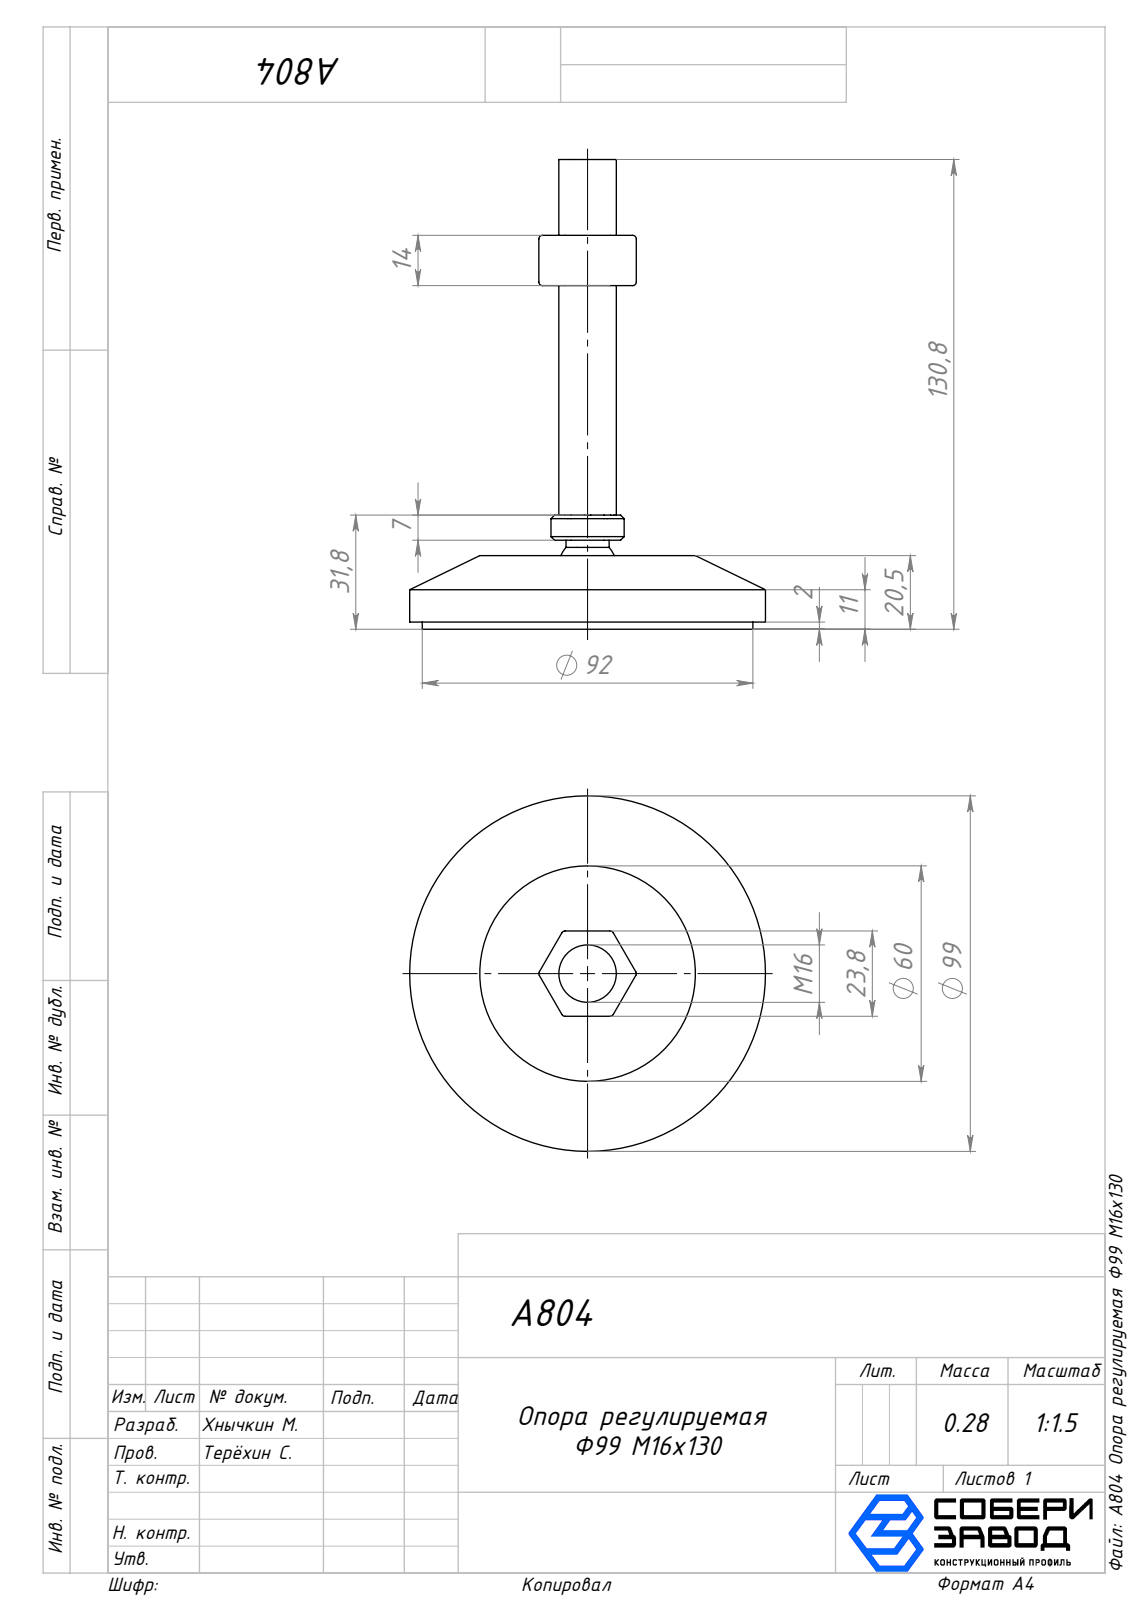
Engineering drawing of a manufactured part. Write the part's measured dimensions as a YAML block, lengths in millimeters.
part_name: "A804 Опора регулируемая Ф99 М16х130; Опора_00; Шарнирный вал M16_00; Гайка М16_00"
step_written_by: "SolidWorks 2025 (AUTOMOTIVE_DESIGN)"
units: millimeters
bodies: {solids: 3, faces: 111, planar: 37, cylindrical: 38, other: 36}
overall_size: [130.79, 99, 99]
volume: 157594
surface_area: 28495
round_holes:
  - {diameter: 14, count: 1}
  - {diameter: 16, count: 1}
round_bosses_or_shafts:
  - {diameter: 99, count: 1}
  - {diameter: 92, count: 1}
  - {diameter: 12, count: 1}
partial_cylinders:
  - {radius: 1, count: 24}
face_to_face_distances: [20.5, 2, 18.5, 23.74, 2.92, 20.82, 95.68, 93.68, 75.18, 109.68]
